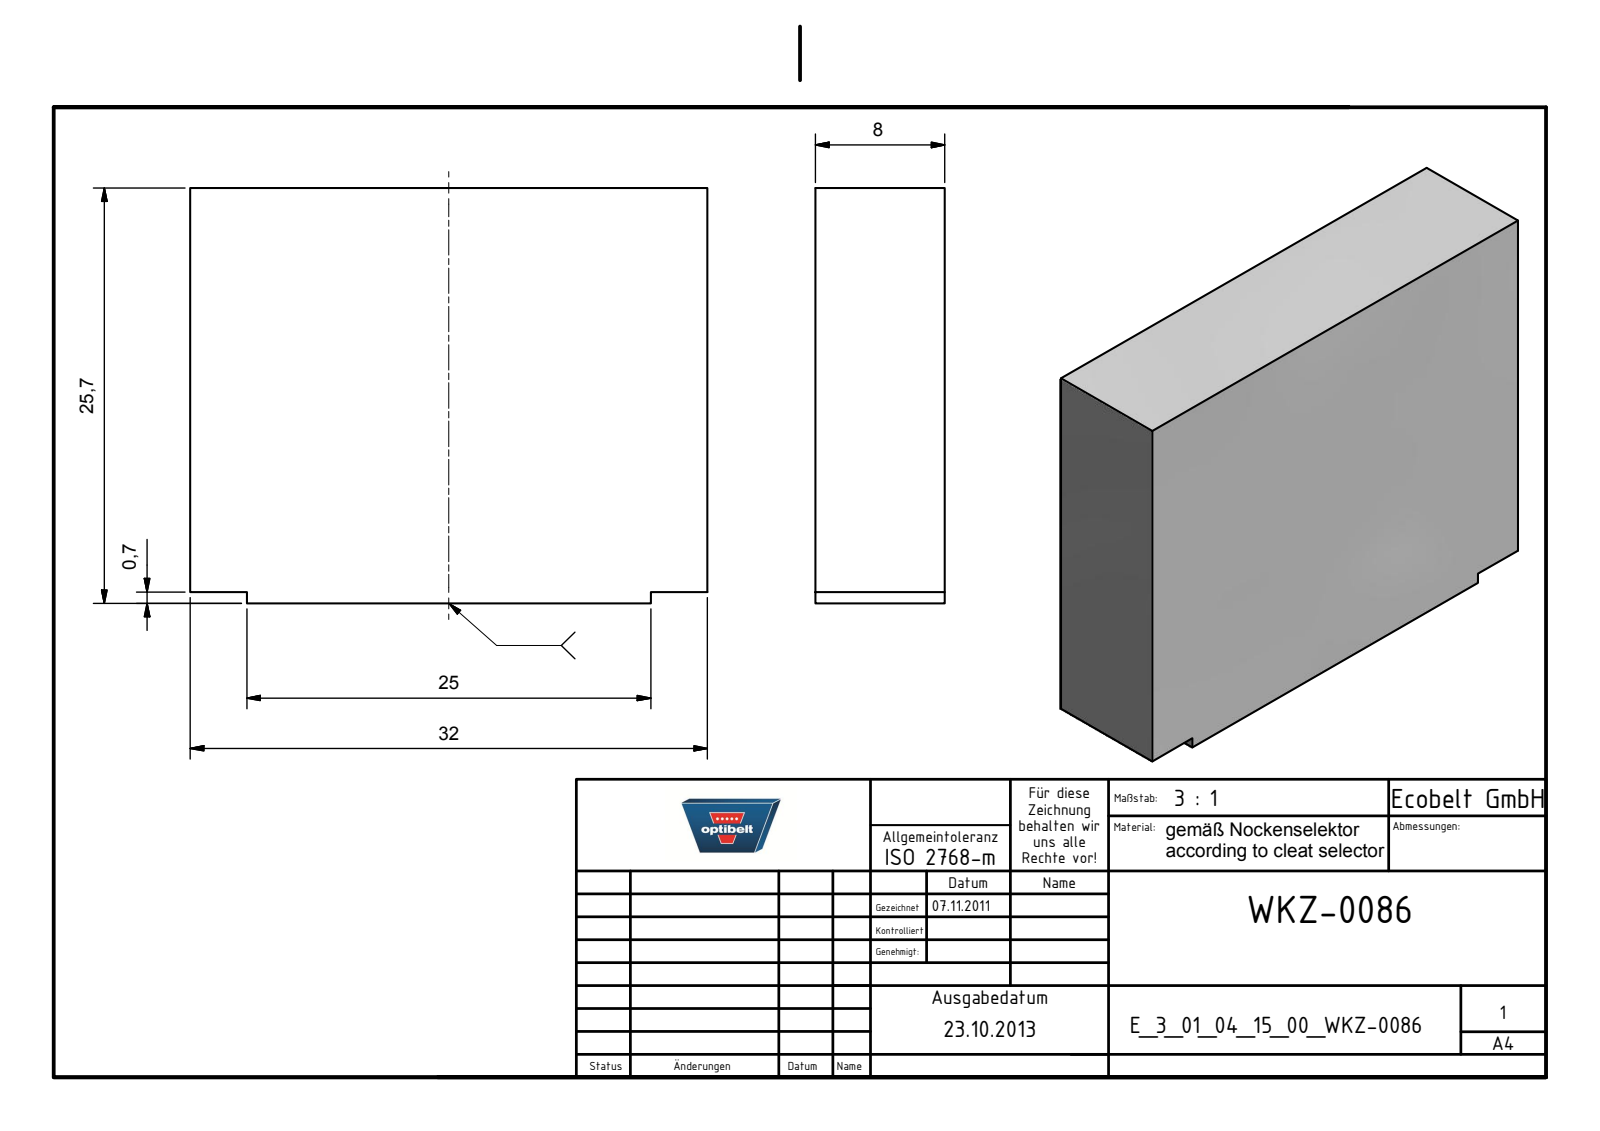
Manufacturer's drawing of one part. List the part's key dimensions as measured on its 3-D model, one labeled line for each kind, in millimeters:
Part name (STEP PRODUCT): E_3_01_04_15_00_WKZ-0086
STEP written by: Autodesk Inventor 2025 (AUTOMOTIVE_DESIGN)
Units: millimetres
Bodies: 1 solid, 10 faces (10 planar, 0 cylindrical, 0 other)
Overall size (bounding box): 32 × 25.7 × 8
Volume: 6 540 mm³ · Surface area: 2 558 mm²
Main face-to-face distances: 8, 25.7, 32, 25, 0.7, 3.5, 28.5
